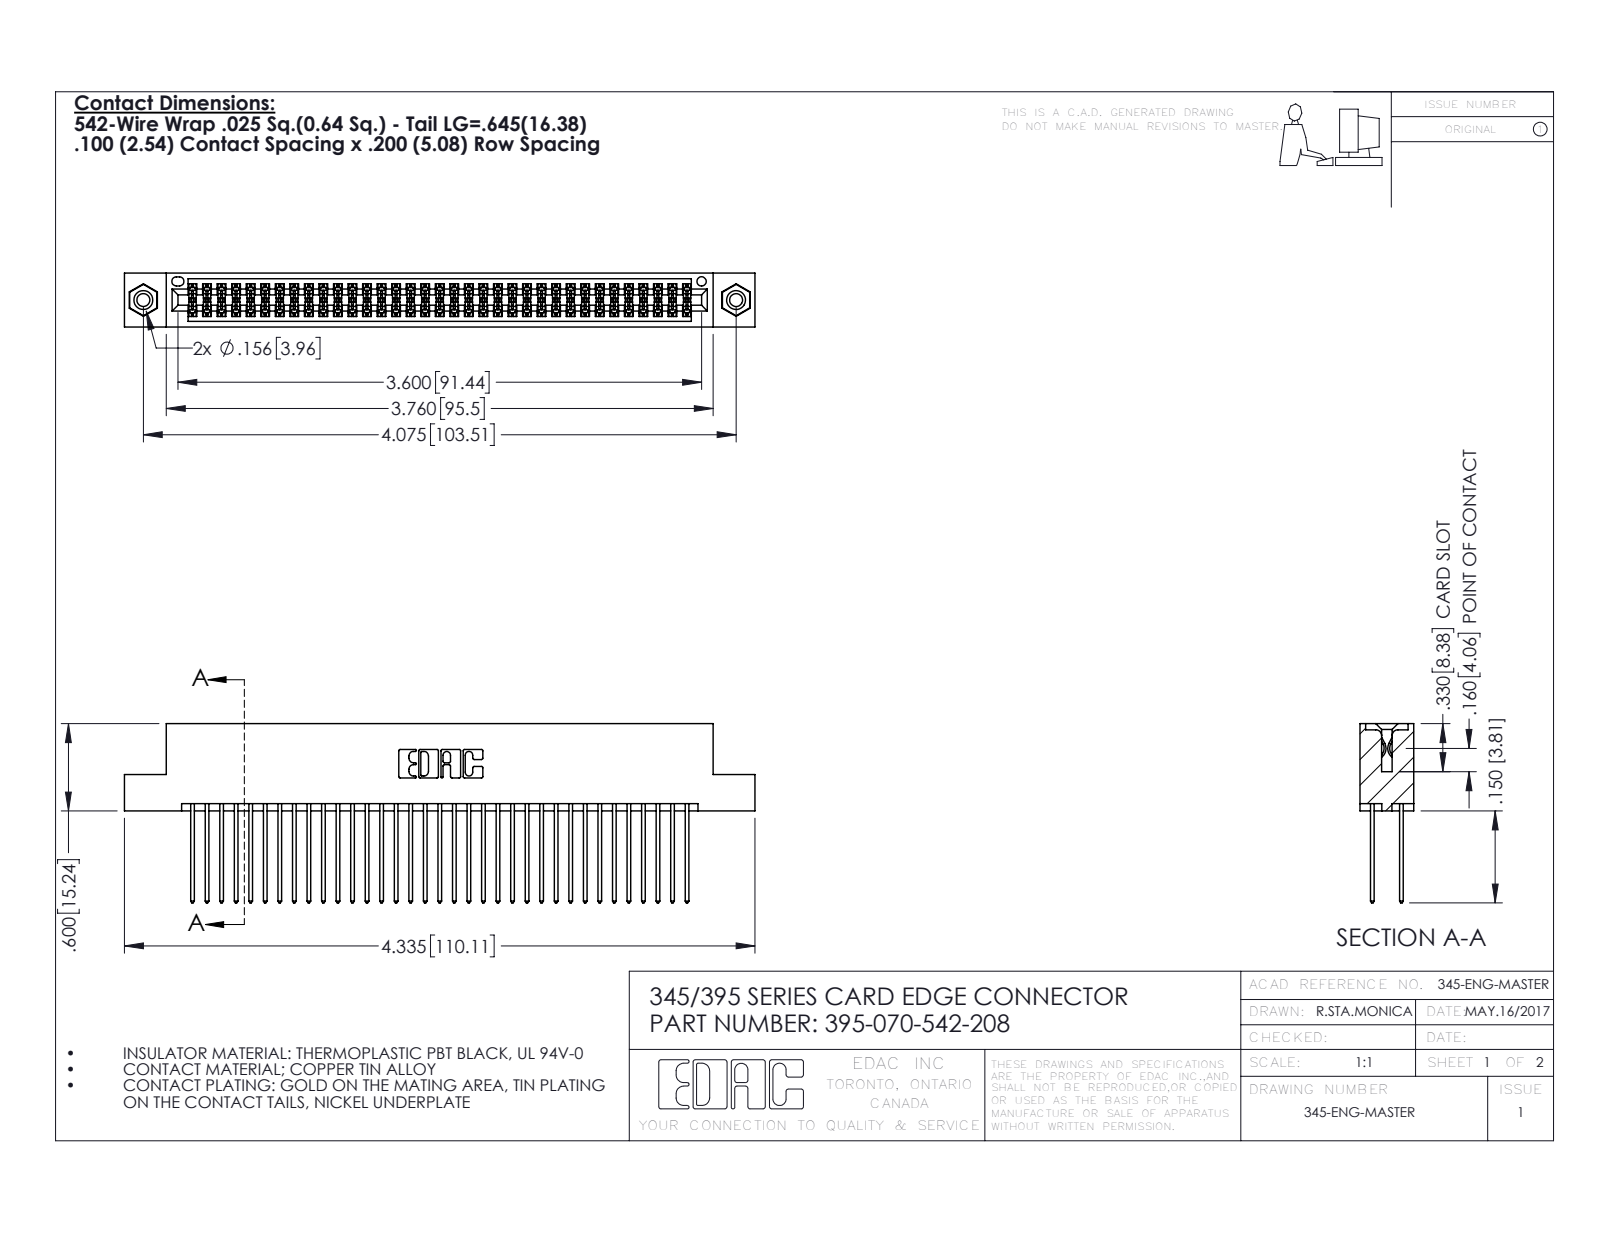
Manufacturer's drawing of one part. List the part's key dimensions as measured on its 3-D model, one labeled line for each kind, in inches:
Part name (STEP PRODUCT): 345-292-001_345-293-142; 345 Part_Flush Mounting Lugs - 0.156 Dia-TI; 395-070-542-208; 345-250-001_345-250-003-102
STEP written by: SolidWorks 2016 (CONFIG_CONTROL_DESIGN)
Units: inches
Bodies: 73 solids, 3686 faces (2422 planar, 1248 cylindrical, 16 other)
Overall size (bounding box): 4.335 × 1.232 × 0.37
Volume: 0.668 in³ · Surface area: 27.26 in²
Round holes (diameter × count): ⌀0.089 ×2, ⌀0.125 ×2, ⌀0.156 ×2, ⌀0.064 ×1
Round bosses / shafts (diameter × count): ⌀0.155 ×2
Partial cylindrical surfaces — rounded edges, fillets, slot ends (radius × count): R0.006 ×105, R0.01 ×70, R0.01 ×22, R0.007 ×6, R0.031 ×6, R0.026 ×3, R0.014 ×2, R0.019 ×2
Main face-to-face distances: 0.072, 0.298, 0.2, 0.098, 0.272, 0.025, 0.37, 0.225, 0.175, 0.149
Hole centre spacings: 0.27, 3.839, 4.075
